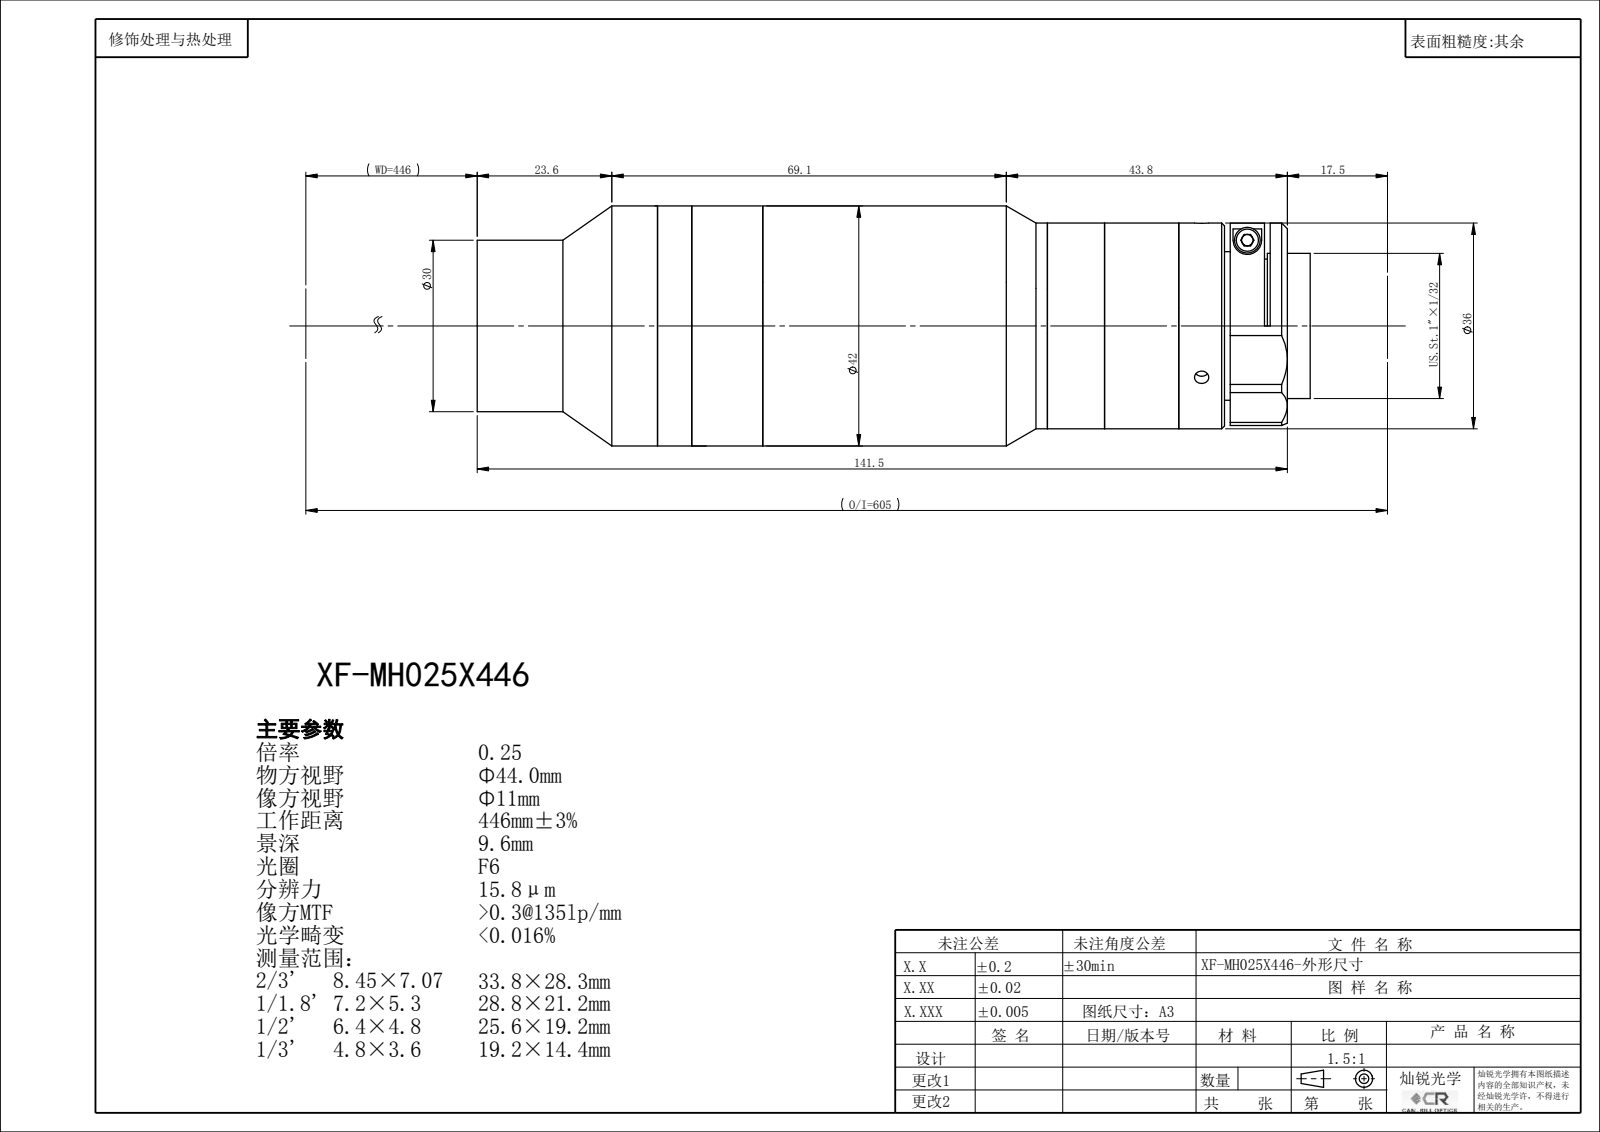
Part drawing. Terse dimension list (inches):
name: XF-MH025X446
written by: SolidWorks 2022 (CONFIG_CONTROL_DESIGN)
unit: in
bodies: 0 solids, 135 faces (69 planar, 48 cylindrical, 18 other)
size: 5.724 × 1.654 × 1.654
holes: 6× ⌀0.098, 1× ⌀0.882, 1× ⌀0.945, 1× ⌀1.039
bosses: 1× ⌀1.654, 1× ⌀1.417, 1× ⌀1.339, 1× ⌀1.181, 1× ⌀1
face distances: 0.731, 0.059, 0.672, 0.236, 0.906, 1.578, 1.637, 1.142, 0.436, 0.495
hole spacings: 0.374
